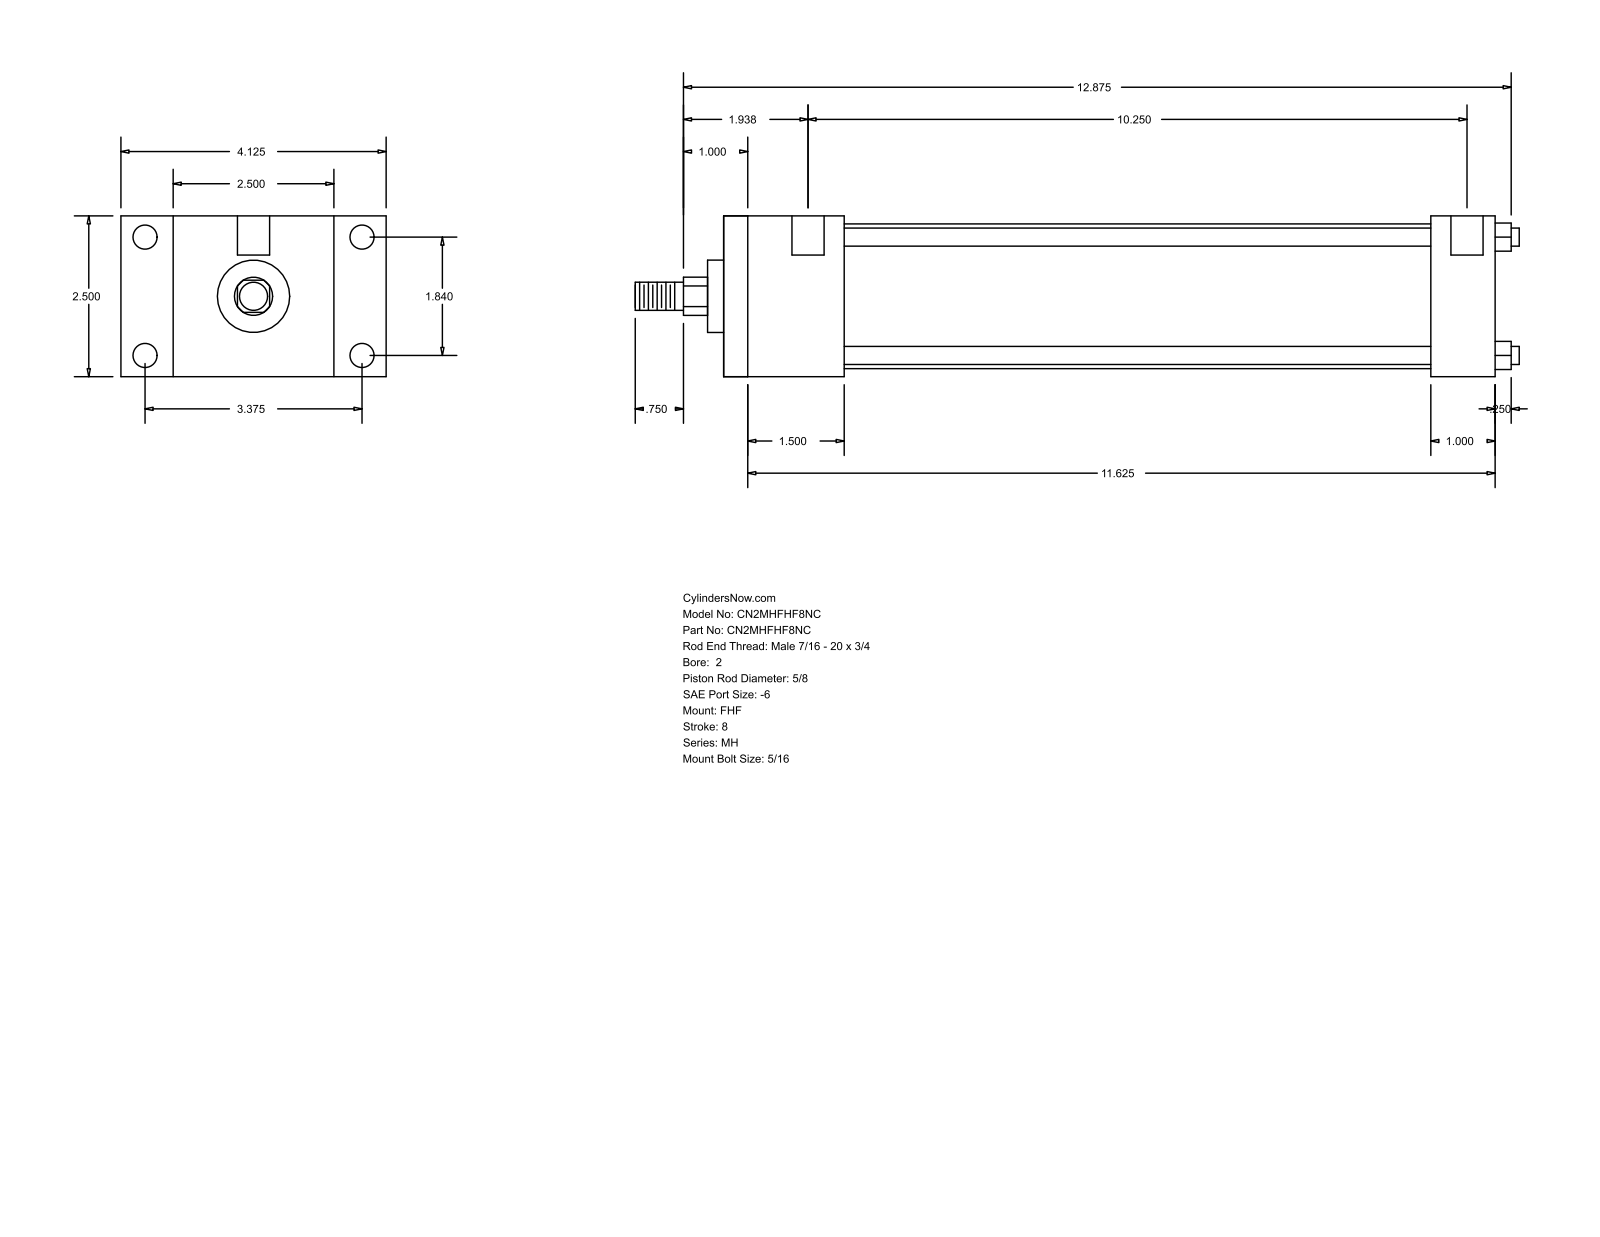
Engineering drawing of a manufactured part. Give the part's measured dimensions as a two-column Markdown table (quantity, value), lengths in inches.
| quantity | value |
| --- | --- |
| part name | MH_FHF__0200_0.625 |
| STEP written by | GSSL Pune (CONFIG_CONTROL_DESIGN) |
| units | inches |
| bodies | 0 solids, 88 faces (60 planar, 28 cylindrical, 0 other) |
| overall size | 13.75 × 4.125 × 2.5 |
| round holes (diameter × count) | 0.219 × 4, 0.375 × 4, 0.5 × 2 |
| round bosses / shafts (diameter × count) | 0.281 × 4, 2.25 × 1, 1.125 × 1, 0.625 × 1, 0.437 × 1 |
| partial cylindrical surfaces (radius × count) | 0.297 × 1 |
| main face-to-face distances | 2.5, 1.875, 12, 10.125, 0.813, 3.313, 4.125, 11, 9.125, 1 |
| hole center spacings | 1.84, 3.375, 3.844, 10.563, 0.125, 0.187, 10.25, 10.375 |
